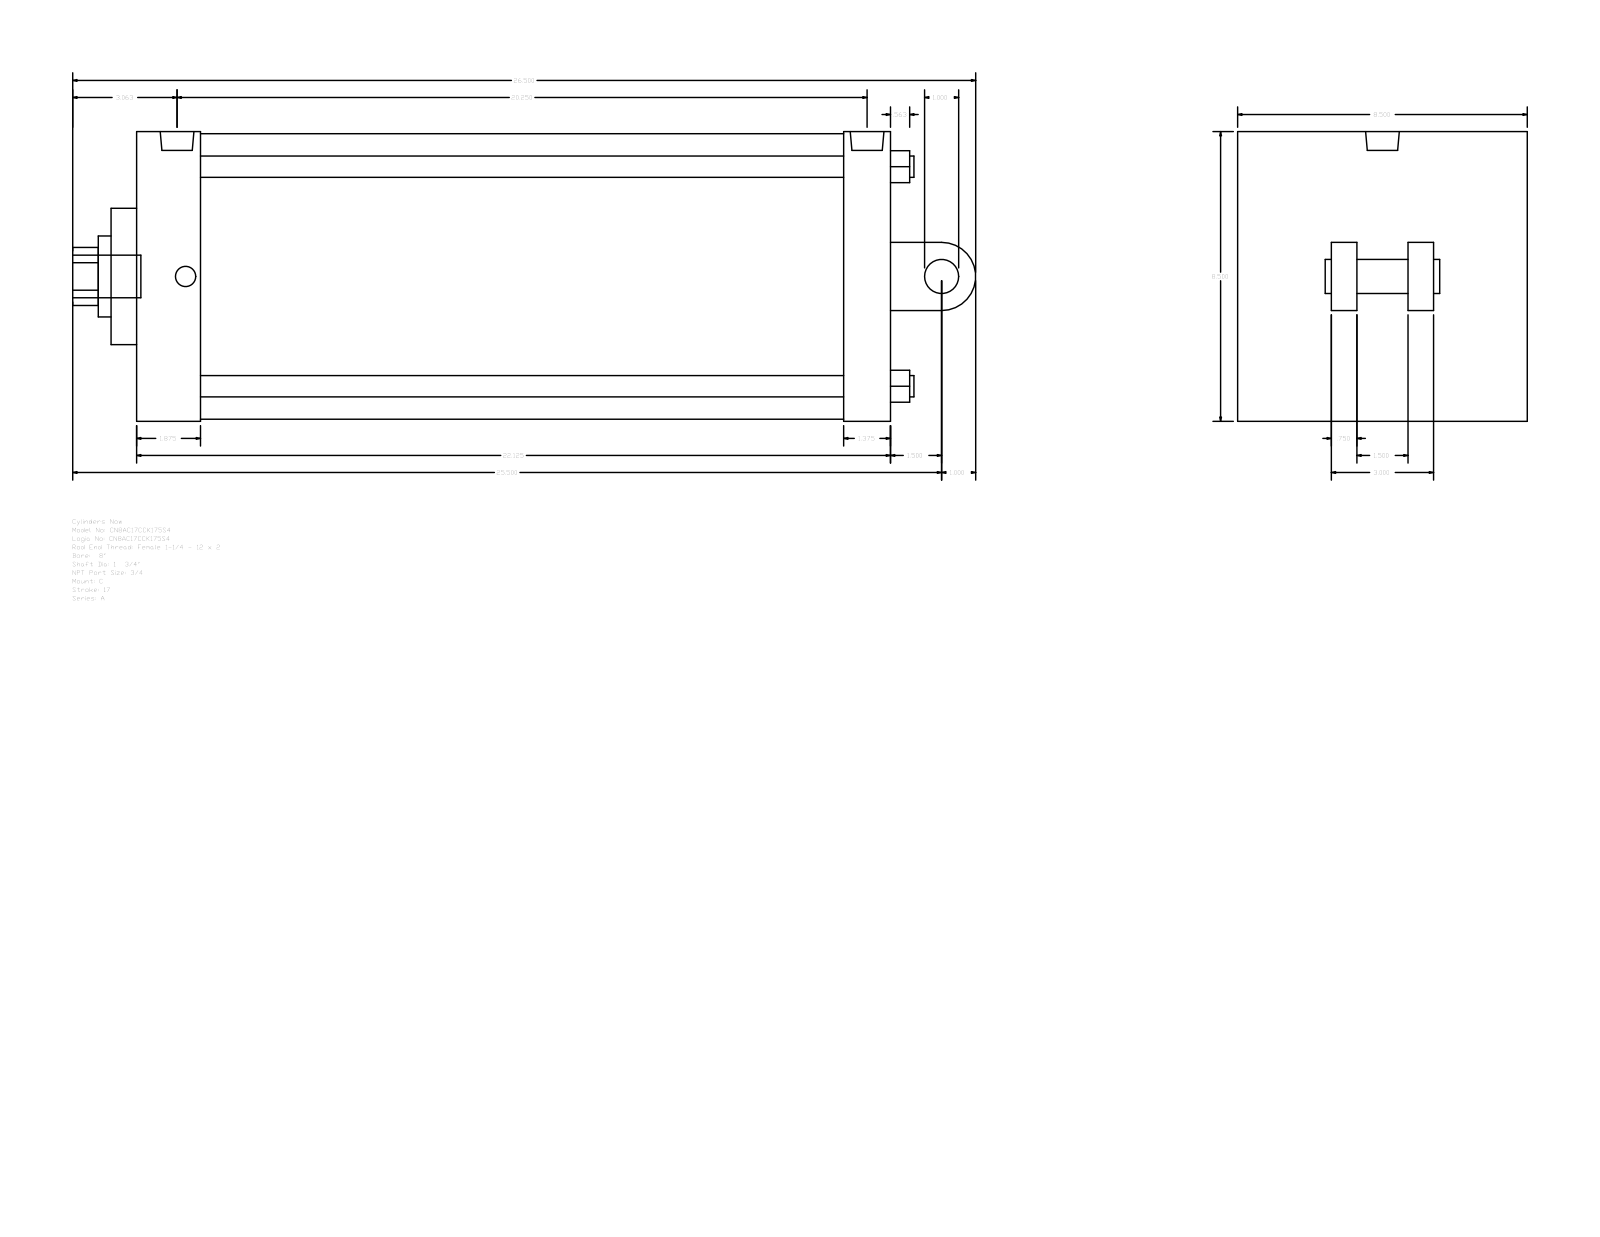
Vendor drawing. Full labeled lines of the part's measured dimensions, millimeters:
Part name (STEP PRODUCT): A_C__0800_1.75
STEP written by: GSSL Pune (CONFIG_CONTROL_DESIGN)
Units: millimetres
Bodies: 0 solids, 104 faces (75 planar, 29 cylindrical, 0 other)
Overall size (bounding box): 673.1 × 215.9 × 215.9
Round holes (diameter × count): ⌀15.88 ×4, ⌀15.08 ×2, ⌀25.12 ×1, ⌀44.45 ×1, ⌀60.33 ×1, ⌀212.72 ×1
Round bosses / shafts (diameter × count): ⌀15.08 ×2, ⌀31.75 ×1, ⌀25.4 ×1, ⌀25.12 ×1
Partial cylindrical surfaces — rounded edges, fillets, slot ends (radius × count): R21.63 ×1, R25.4 ×1
Main face-to-face distances: 561.98, 215.9, 19.05, 57.15, 47.63, 514.35, 527.05, 479.42, 34.93, 88.9
Hole centre spacings: 115.67, 163.58, 231.34, 6.35
